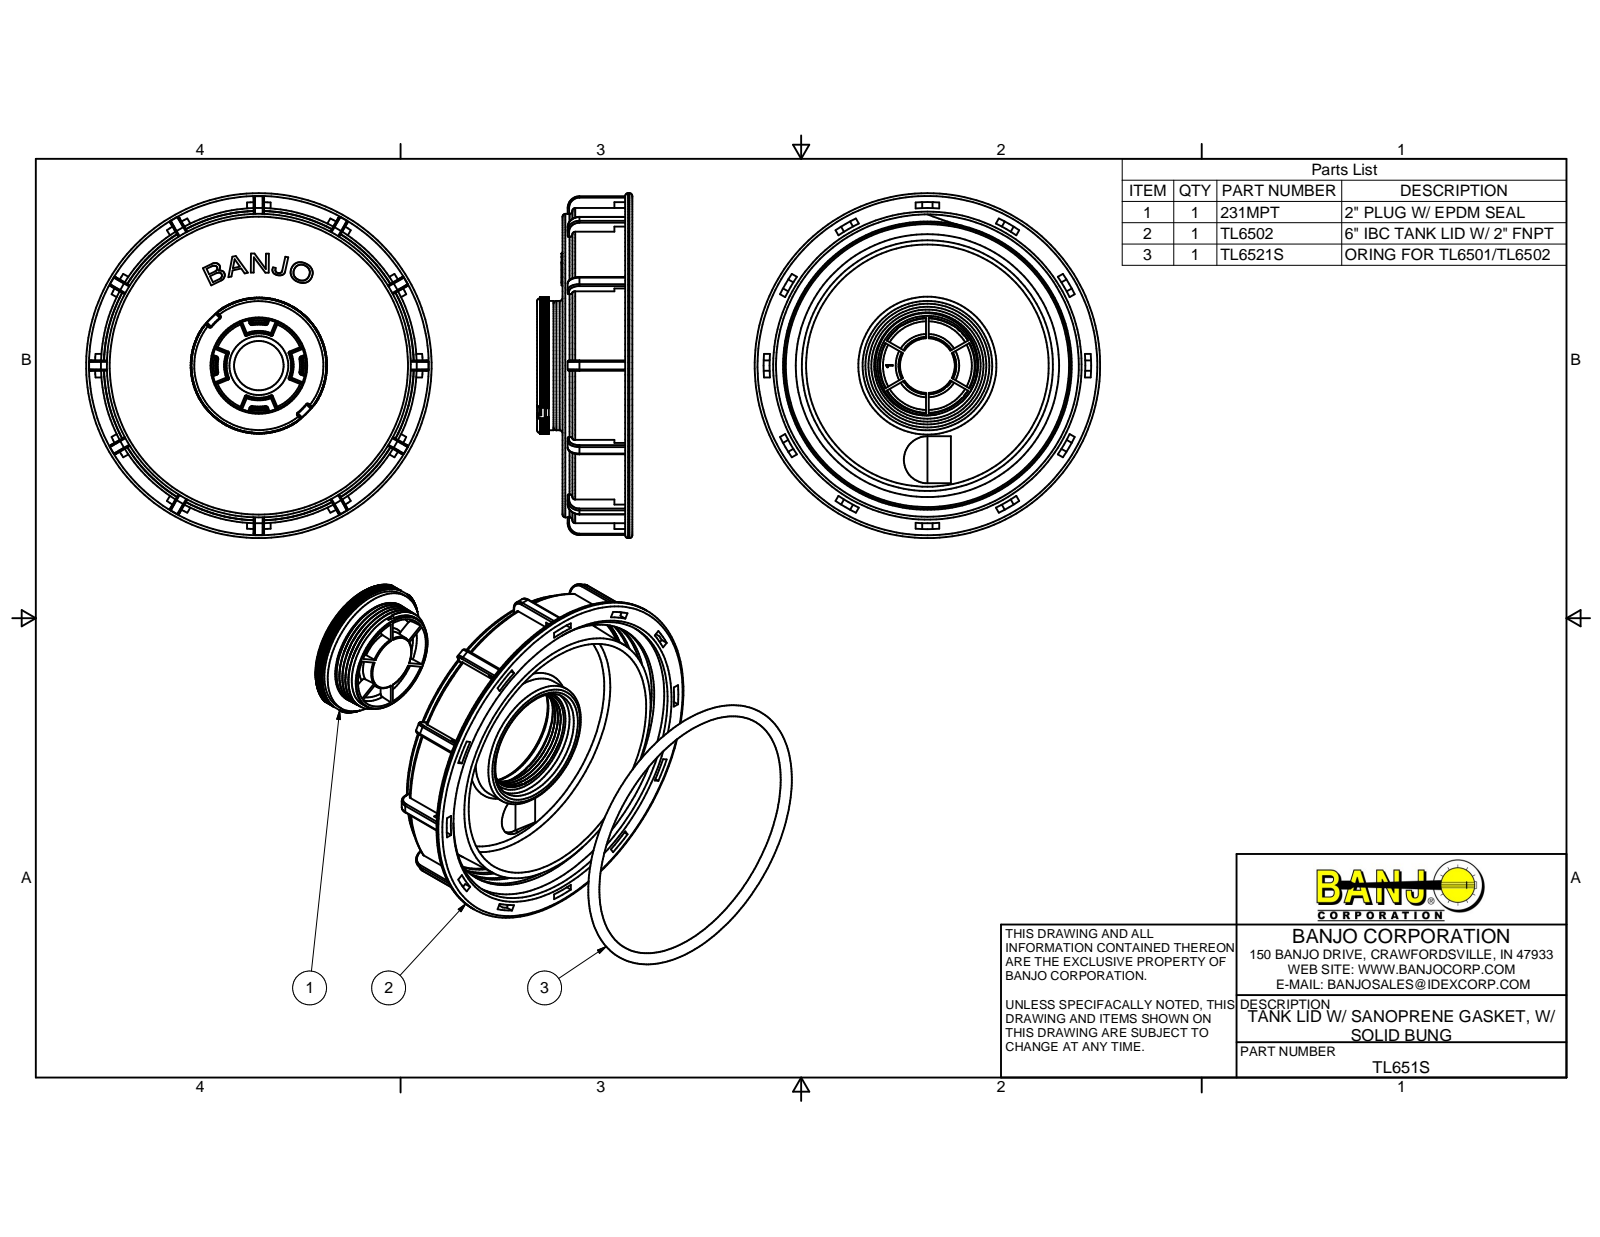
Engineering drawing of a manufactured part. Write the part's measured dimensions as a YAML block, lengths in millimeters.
part_name: "TL651S; TL6502; TL6521S; 231MPT (+2 more)"
step_written_by: "Autodesk Inventor 2022 (AUTOMOTIVE_DESIGN)"
units: millimeters
bodies: {solids: 4, faces: 1861, planar: 1000, cylindrical: 641, other: 220}
overall_size: [186.2, 186.2, 51.3]
volume: 314000
surface_area: 162200
round_holes:
  - {diameter: 26.7, count: 1}
  - {diameter: 50.5, count: 1}
  - {diameter: 58.4, count: 1}
  - {diameter: 60.5, count: 1}
  - {diameter: 135.3, count: 1}
  - {diameter: 154.2, count: 1}
  - {diameter: 155.6, count: 1}
  - {diameter: 163.2, count: 1}
round_bosses_or_shafts:
  - {diameter: 186.2, count: 1}
  - {diameter: 170.2, count: 1}
  - {diameter: 163.8, count: 1}
  - {diameter: 69.9, count: 1}
partial_cylinders:
  - {radius: 0.8, count: 68}
  - {radius: 6.4, count: 12}
  - {radius: 0.4, count: 2}
  - {radius: 12.7, count: 1}
  - {radius: 15.2, count: 1}
  - {radius: 24.4, count: 1}
  - {radius: 33.3, count: 1}
  - {radius: 36.3, count: 1}
face_to_face_distances: [4.1, 37.6, 33.5, 7.4, 8.9, 33.8, 29.7, 3.8, 11.4, 41.1]
